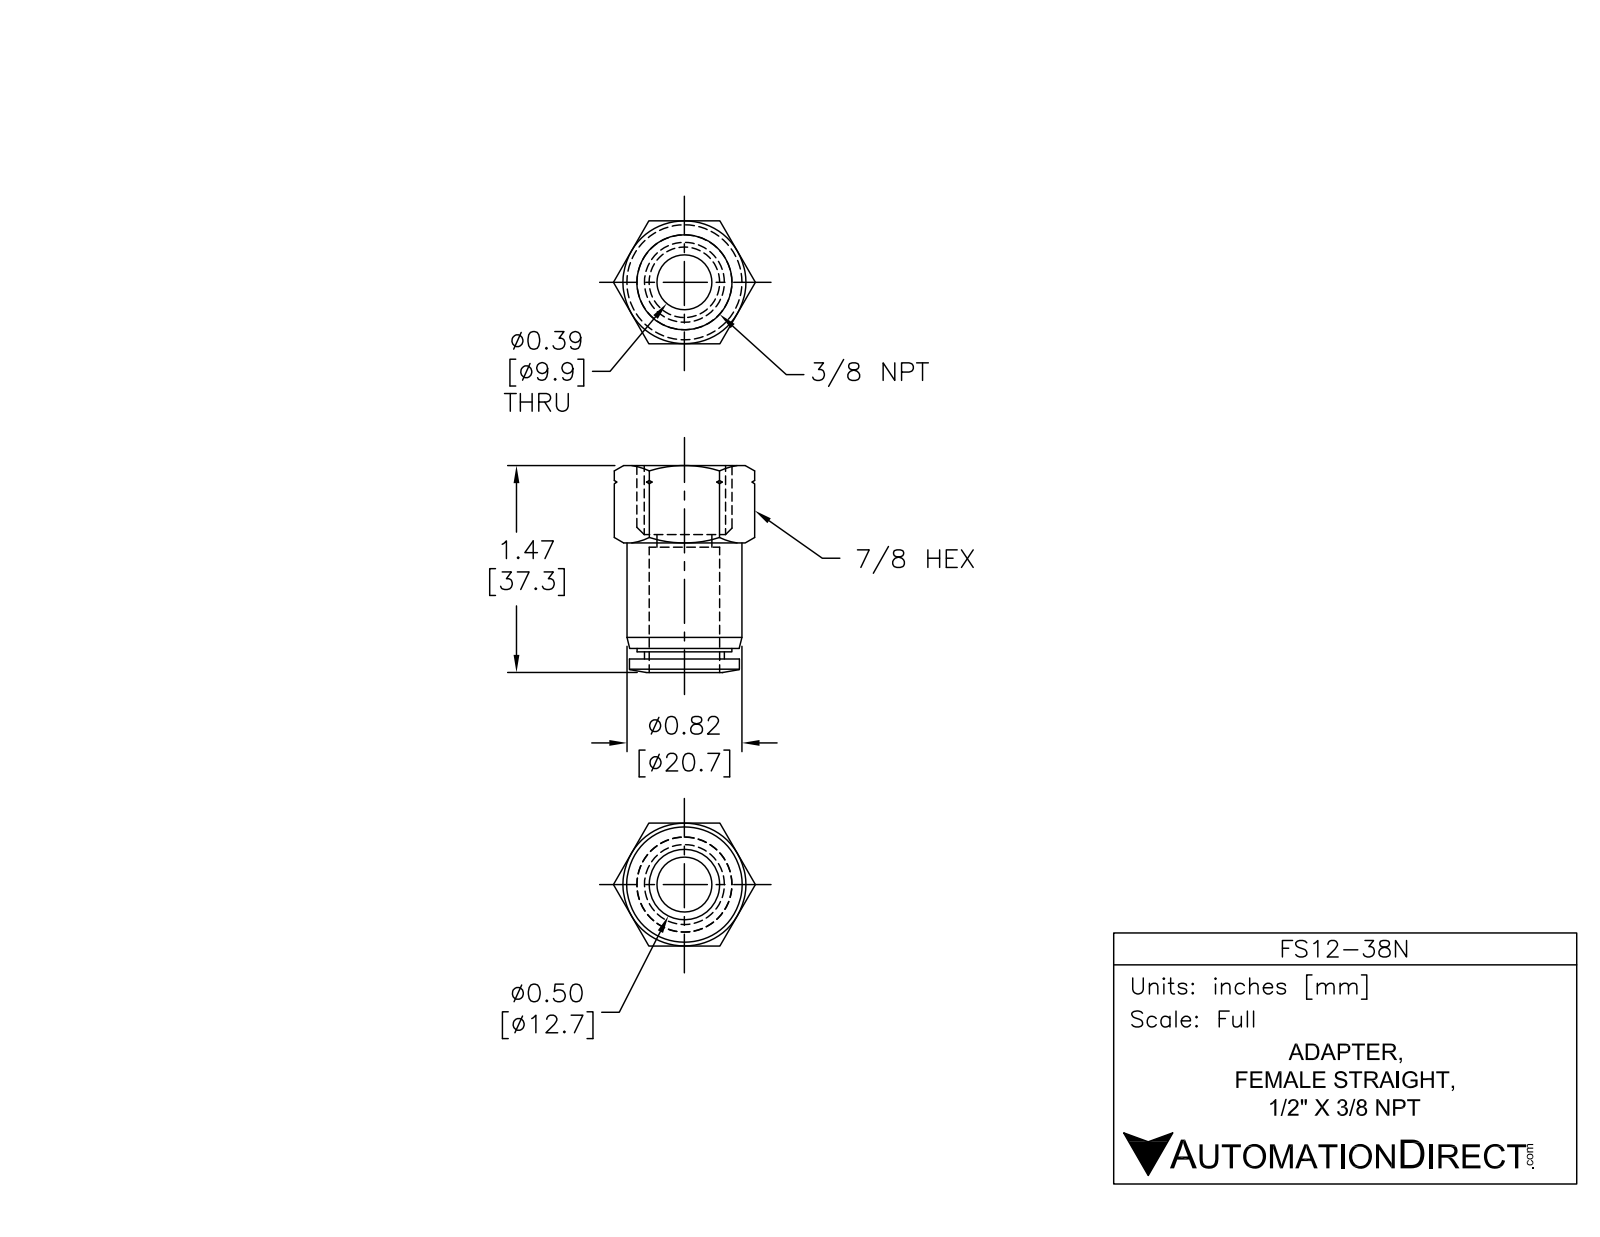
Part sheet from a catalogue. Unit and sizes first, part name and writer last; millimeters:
Units: millimetres
Overall size (bounding box): 37.4 × 25.4 × 22
Round holes (diameter × count): ⌀10 ×1, ⌀13 ×1
Round bosses / shafts (diameter × count): ⌀20.8 ×1, ⌀19.9 ×1, ⌀17.1 ×1, ⌀14.5 ×1
Main face-to-face distances: 22, 35, 12.5, 22.5, 33.1, 20.6, 1.9, 33.7, 21.2, 0.6
Volume: 7 440 mm³ · Surface area: 5 057 mm²
Bodies: 1 solid, 61 faces (13 planar, 12 cylindrical, 36 other)
Part name (STEP PRODUCT): FS12-38N
STEP written by: SolidWorks 2015 (AUTOMOTIVE_DESIGN)
